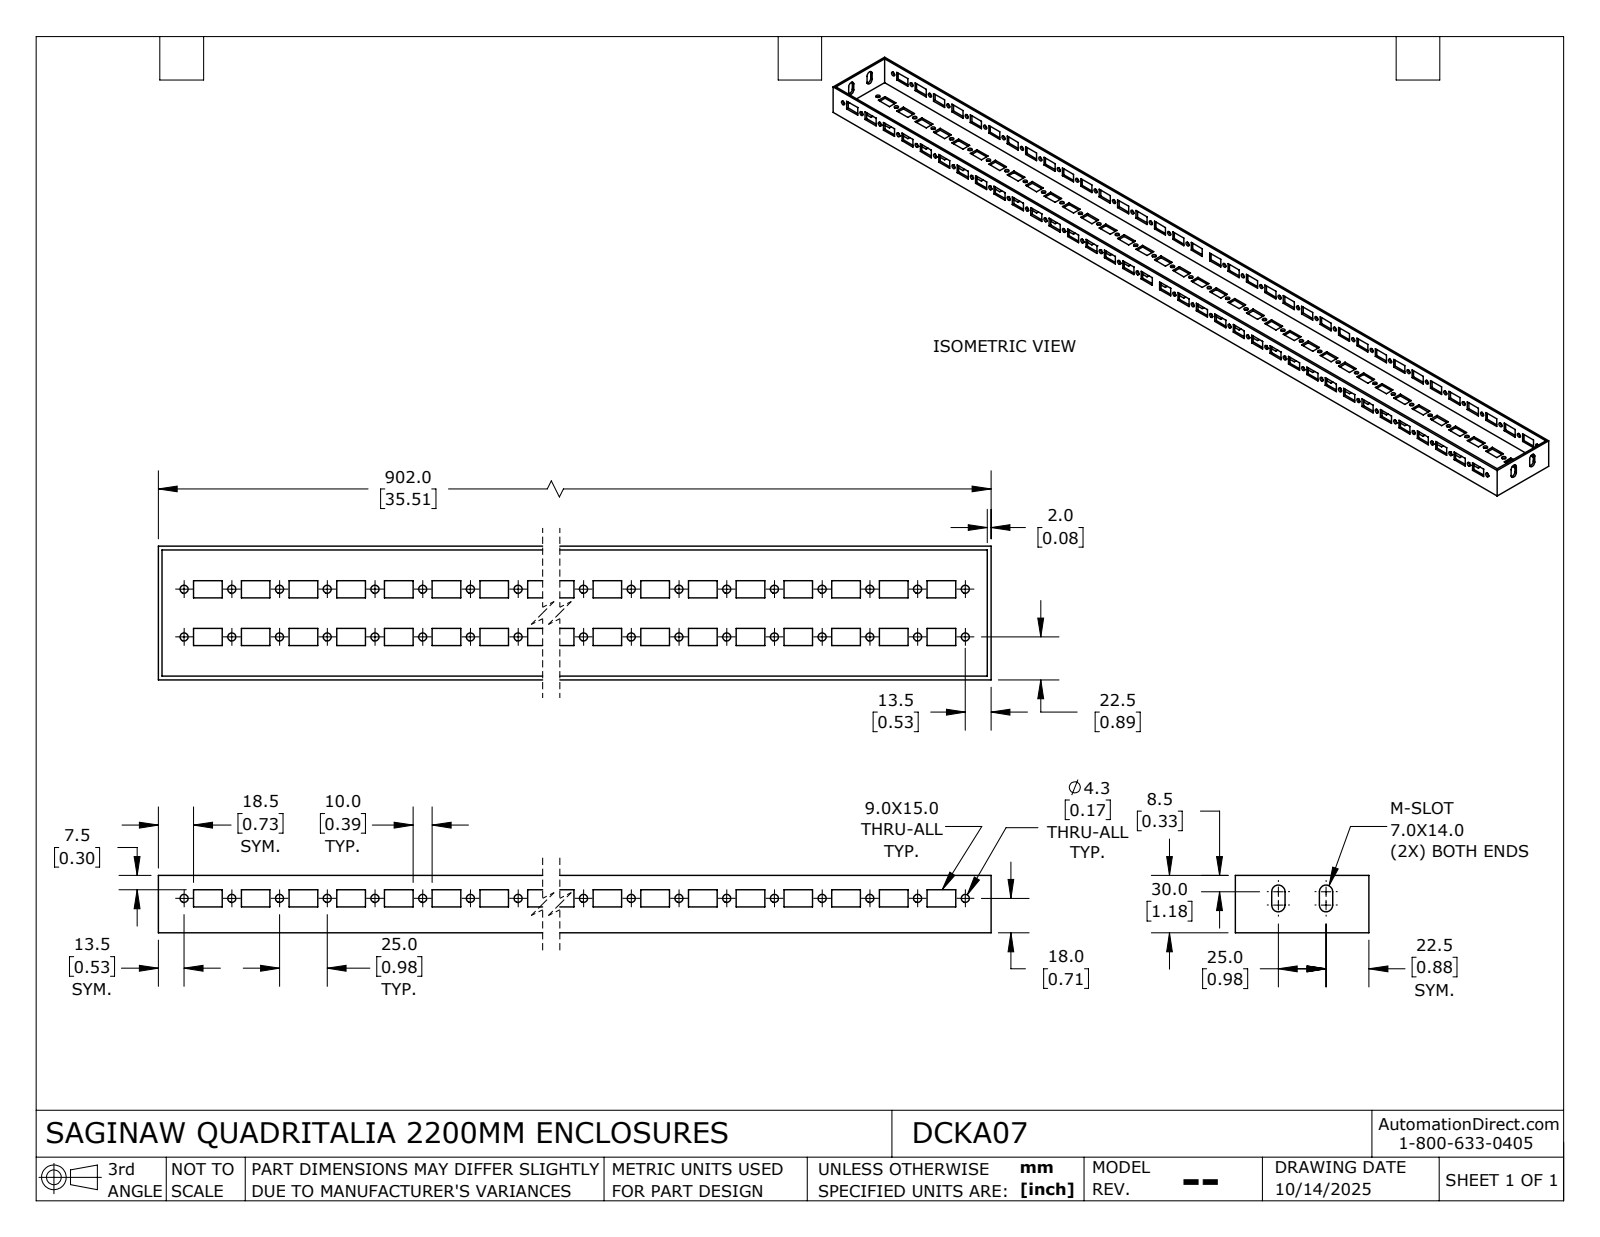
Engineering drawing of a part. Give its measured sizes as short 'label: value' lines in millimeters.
name: DCKA07_Default
written by: SolidWorks 2024 (CONFIG_CONTROL_DESIGN)
unit: mm
bodies: 1 solid, 729 faces (579 planar, 150 cylindrical, 0 other)
size: 902 × 70 × 30
volume: 192 167 mm³; area: 213 575 mm²
holes: 107× ⌀4.25
rounds: 4× R3.5
face distances: 2, 68, 70, 66, 25, 9, 30, 28, 900, 16
hole spacings: 25, 50, 75, 100, 125, 150, 175, 200
